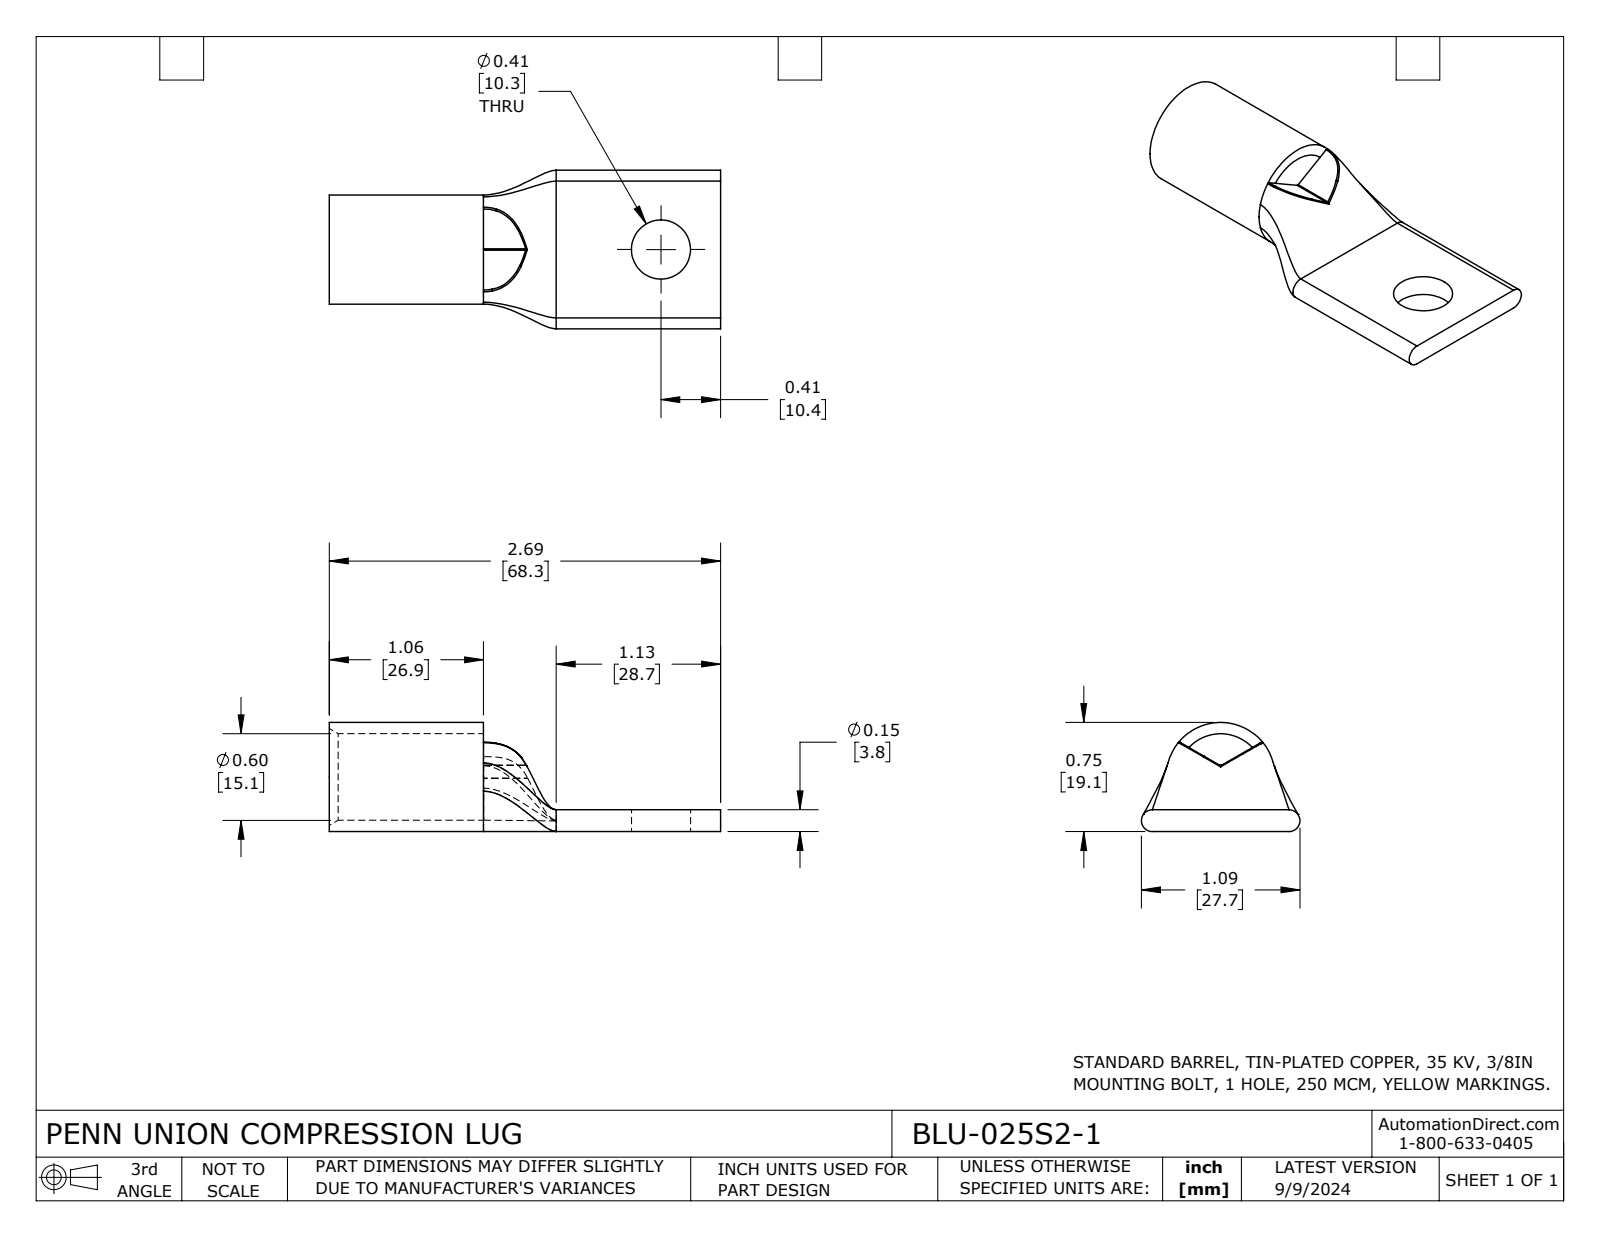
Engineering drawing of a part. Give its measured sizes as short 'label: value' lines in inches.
name: BLU-025S2-1
written by: SolidWorks 2023 (CONFIG_CONTROL_DESIGN)
unit: in
bodies: 1 solid, 39 faces (11 planar, 11 cylindrical, 17 other)
size: 2.69 × 1.09 × 0.75
volume: 0.406 in³; area: 9.841 in²
holes: 1× ⌀0.406, 1× ⌀0.595
bosses: 1× ⌀0.75
rounds: 2× R0.01, 2× R0.075
face distances: 0.15, 0.078, 2.69, 1.06, 1.63, 1.56, 0.5, 1.13
